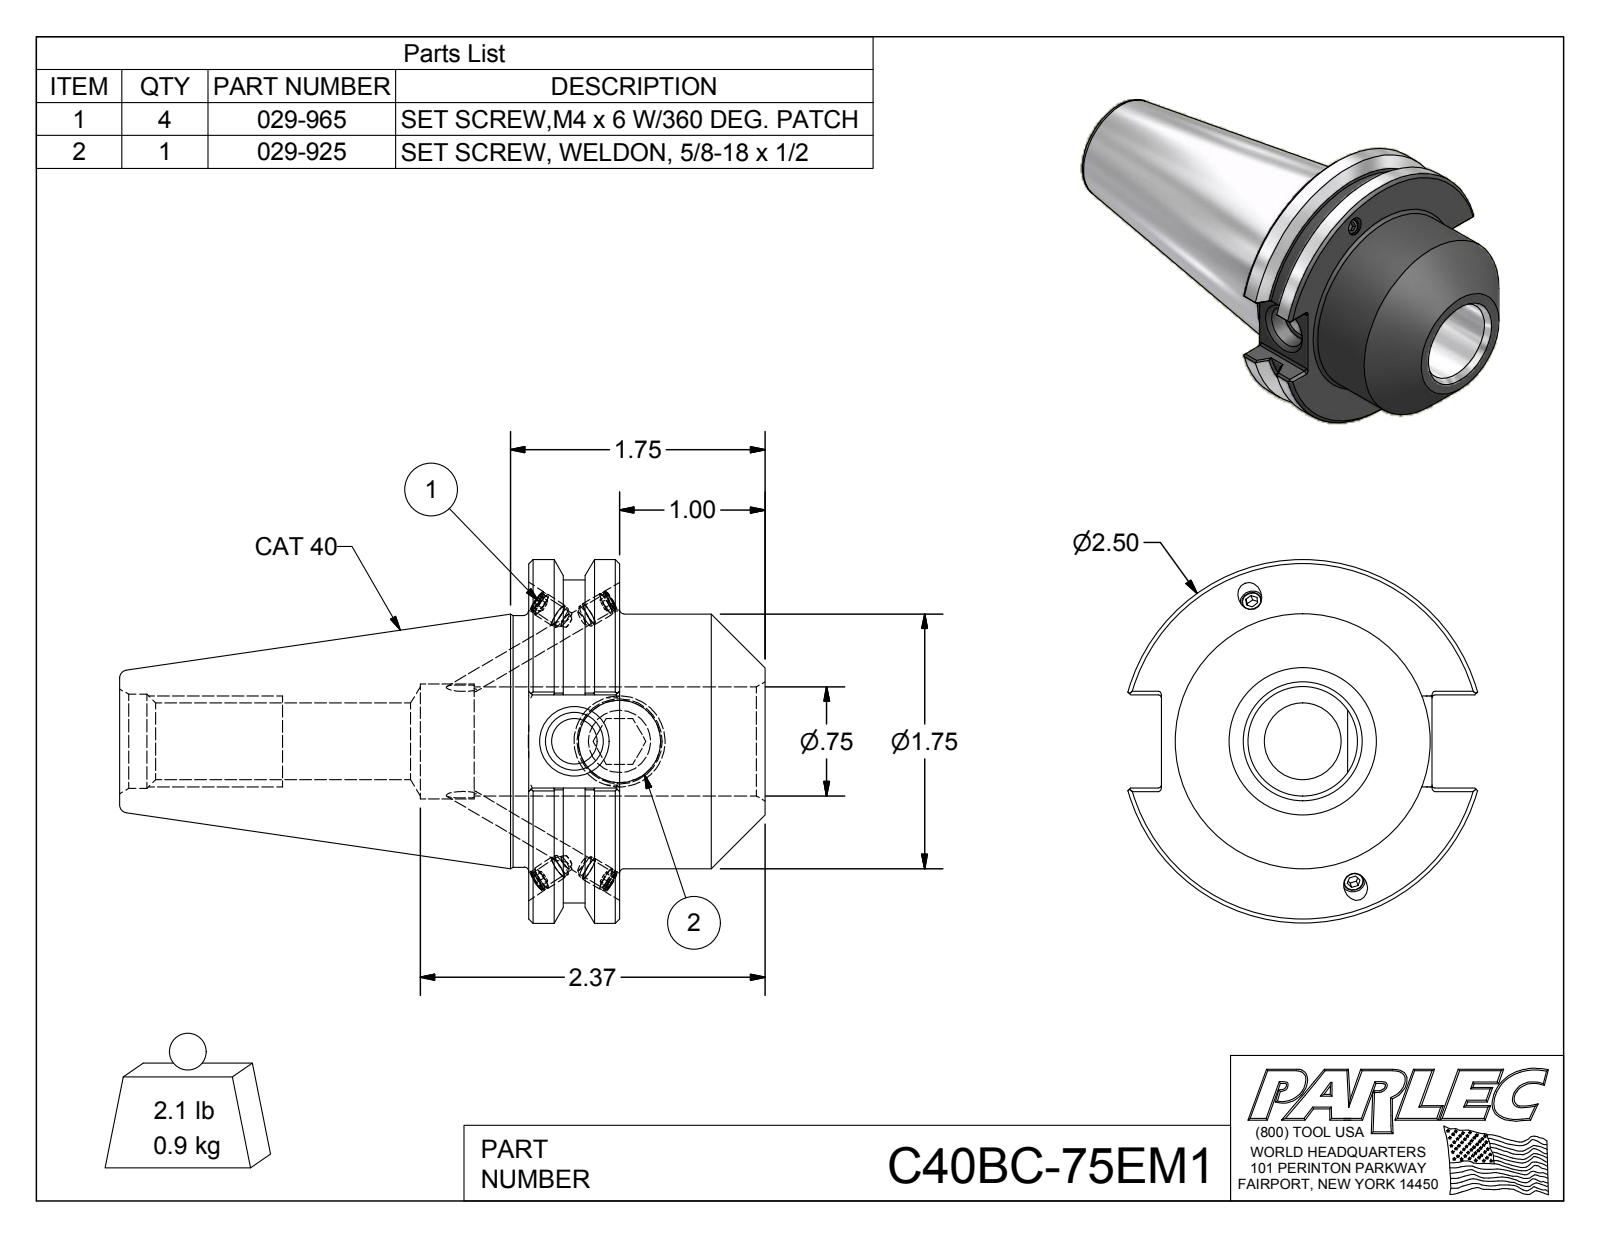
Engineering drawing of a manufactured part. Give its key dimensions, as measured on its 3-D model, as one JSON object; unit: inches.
{"part_name": "C40BC-75EM1; C40BC-75EM1-1; 029-965; 029-925", "step_written_by": "Autodesk Inventor 2012 (AUTOMOTIVE_DESIGN)", "units": "inches", "bodies": {"solids": 6, "faces": 187, "planar": 92, "cylindrical": 49, "other": 46}, "overall_size": [4.437, 2.5, 2.406], "volume_in3": 7.379, "surface_area_in2": 42.84, "round_holes": [[0.13, 4], [0.161, 4], [0.315, 1], [0.399, 1], [0.527, 1], [0.565, 1], [0.625, 1], [0.648, 1], [0.75, 1], [0.79, 1]], "round_bosses_or_shafts": [[0.165, 4], [0.157, 4], [2.5, 1], [2.219, 1], [1.75, 1], [1.73, 1]], "partial_cylinders_radius": [[0.02, 12]], "face_to_face_distances": [0.625, 1, 1.625, 0.08, 0.64, 0.315, 1.86, 1.78, 2.812, 3.437], "hole_center_spacings": [0.31]}
